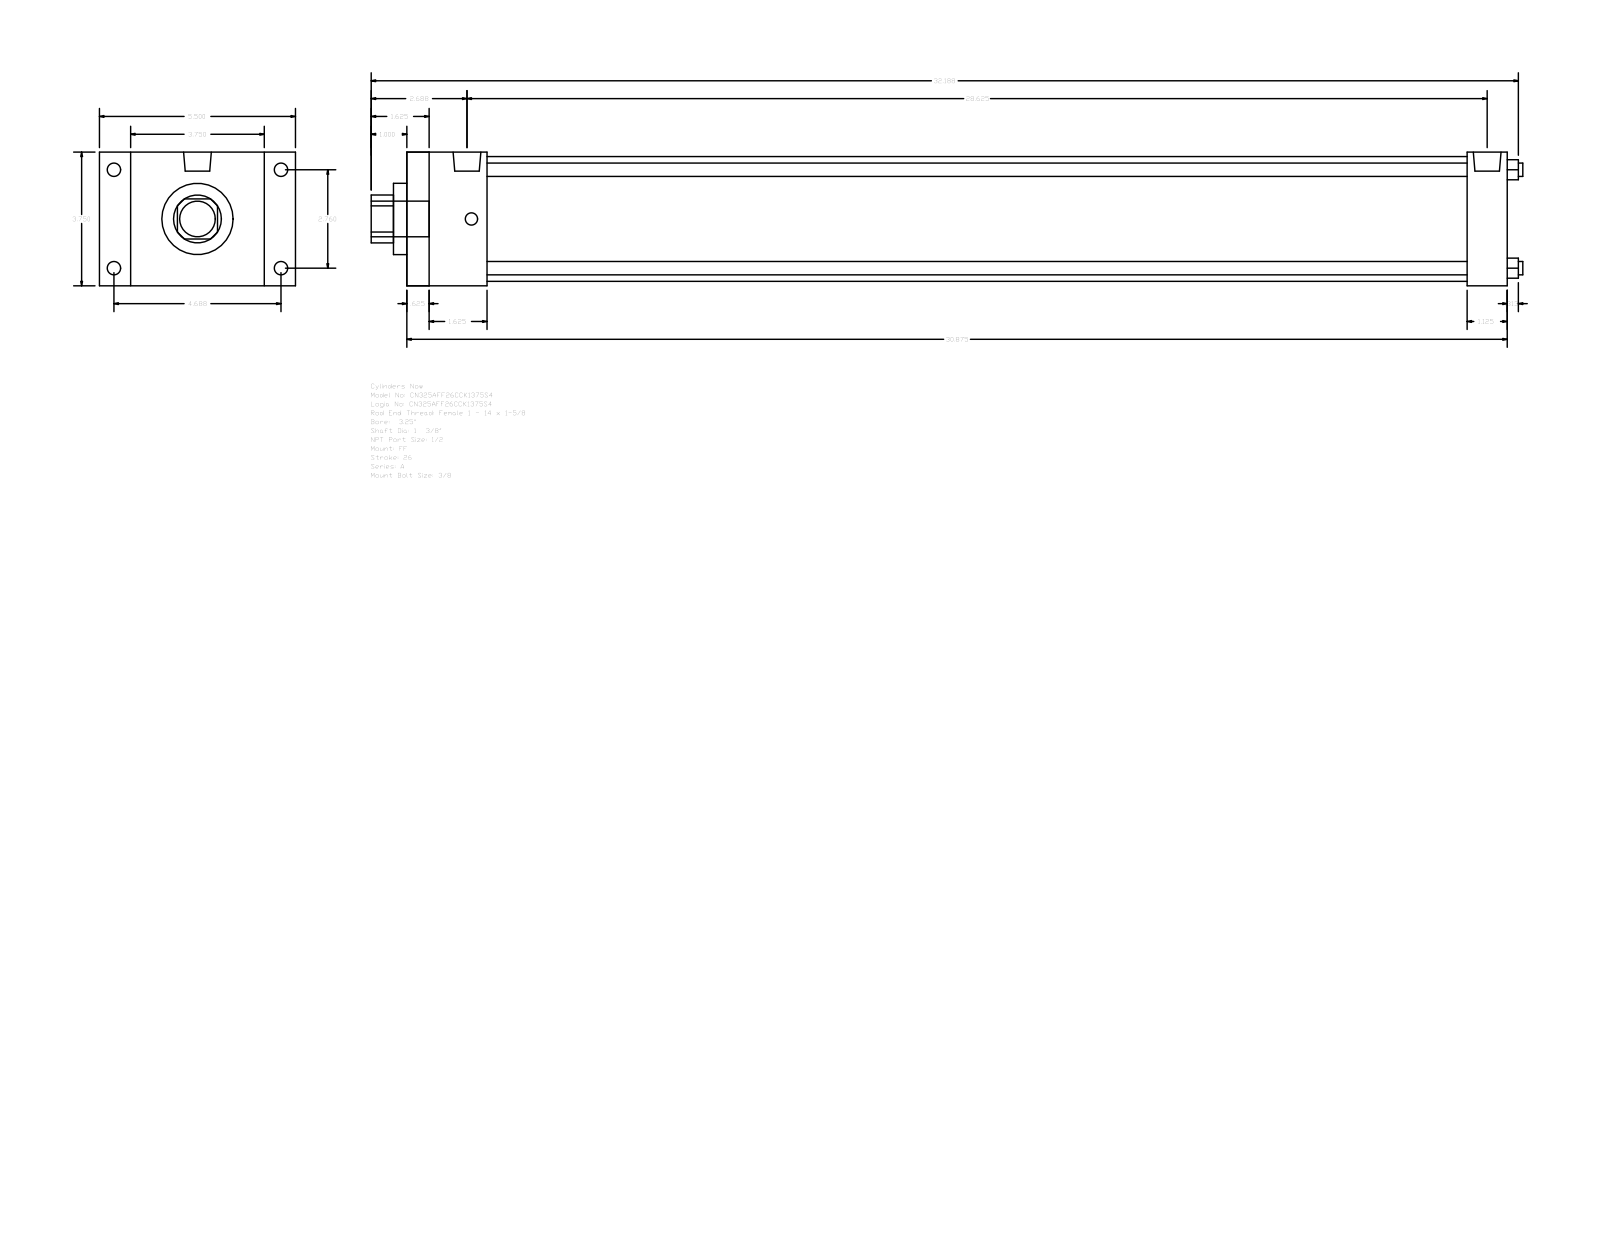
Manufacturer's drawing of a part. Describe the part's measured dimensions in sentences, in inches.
The part is named "A_FF__0325_1.375". Its 3-D file was written by "GSSL Pune (CONFIG_CONTROL_DESIGN)". It is 0 solids with 92 faces: 64 planar, 28 cylindrical and 0 other. Overall it measures 32.313 by 5.5 by 3.75 inches. Round holes: 4 of diameter 0.375, 1 of diameter 1.375, 1 of diameter 2, 1 of diameter 3.5. Round bosses or shafts: 4 of diameter 0.375, 4 of diameter 0.344, 2 of diameter 0.778, 1 of diameter 1. Partial cylindrical surfaces (rounded edges, fillets, slot ends): 1 of radius 0.672. The main face-to-face distances are 3.75, 30.875, 30.25, 0.625, 0.875, 4.625, 1.125, 2.25, 29.75, 1.625. The hole center spacings are 1.952, 2.76, 3.903.
